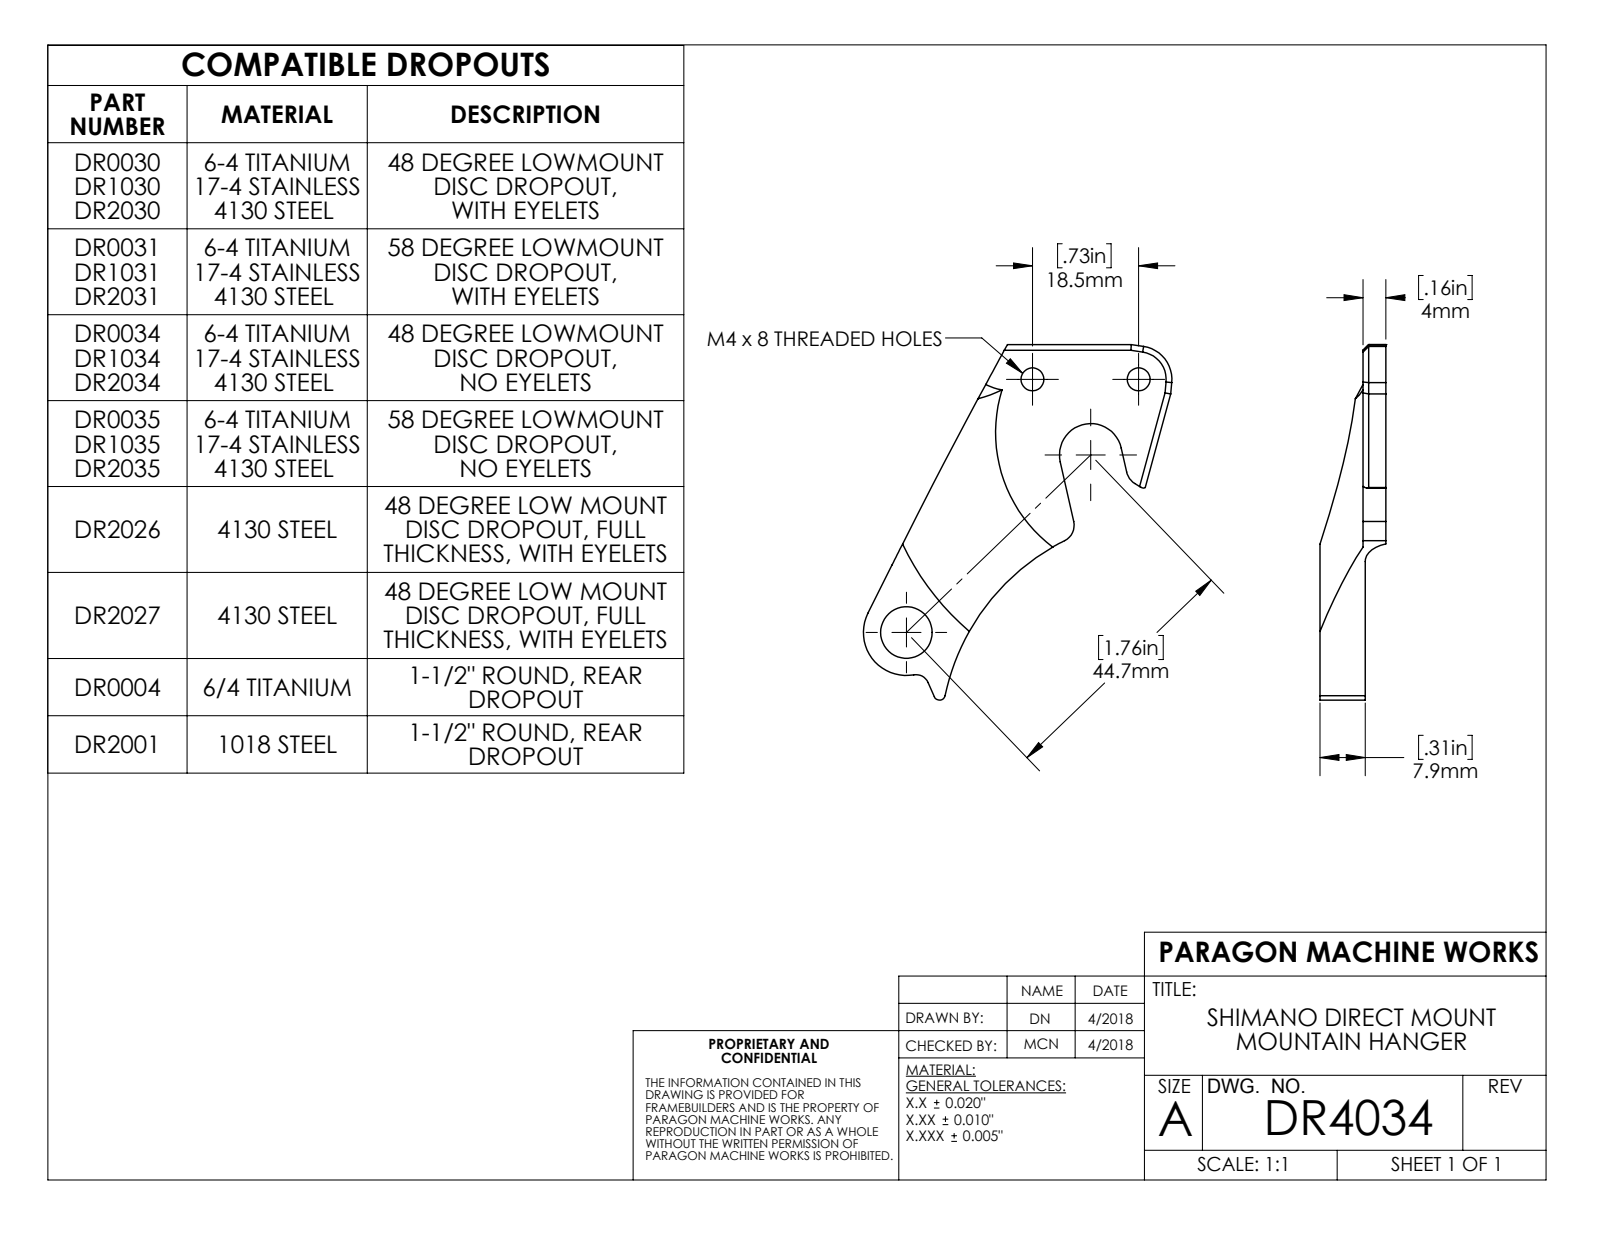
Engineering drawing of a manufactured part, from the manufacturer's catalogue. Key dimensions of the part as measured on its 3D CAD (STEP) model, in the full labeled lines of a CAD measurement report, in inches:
Part name (STEP PRODUCT): DR4034
STEP written by: SolidWorks 2012 (CONFIG_CONTROL_DESIGN)
Units: inches
Bodies: 1 solid, 35 faces (17 planar, 14 cylindrical, 4 other)
Overall size (bounding box): 2.378 × 2.121 × 0.453
Volume: 0.39 in³ · Surface area: 6.388 in²
Round holes (diameter × count): ⌀0.157 ×2, ⌀0.354 ×1
Partial cylindrical surfaces — rounded edges, fillets, slot ends (radius × count): R0.02 ×1, R0.03 ×1, R0.09 ×1, R0.118 ×1, R0.125 ×1, R0.215 ×1, R0.229 ×1, R0.295 ×1
Main face-to-face distances: 0.157, 0.142, 0.016, 0.453, 0.311, 0.295, 0.43
Hole centre spacings: 0.73, 1.944, 2.361
